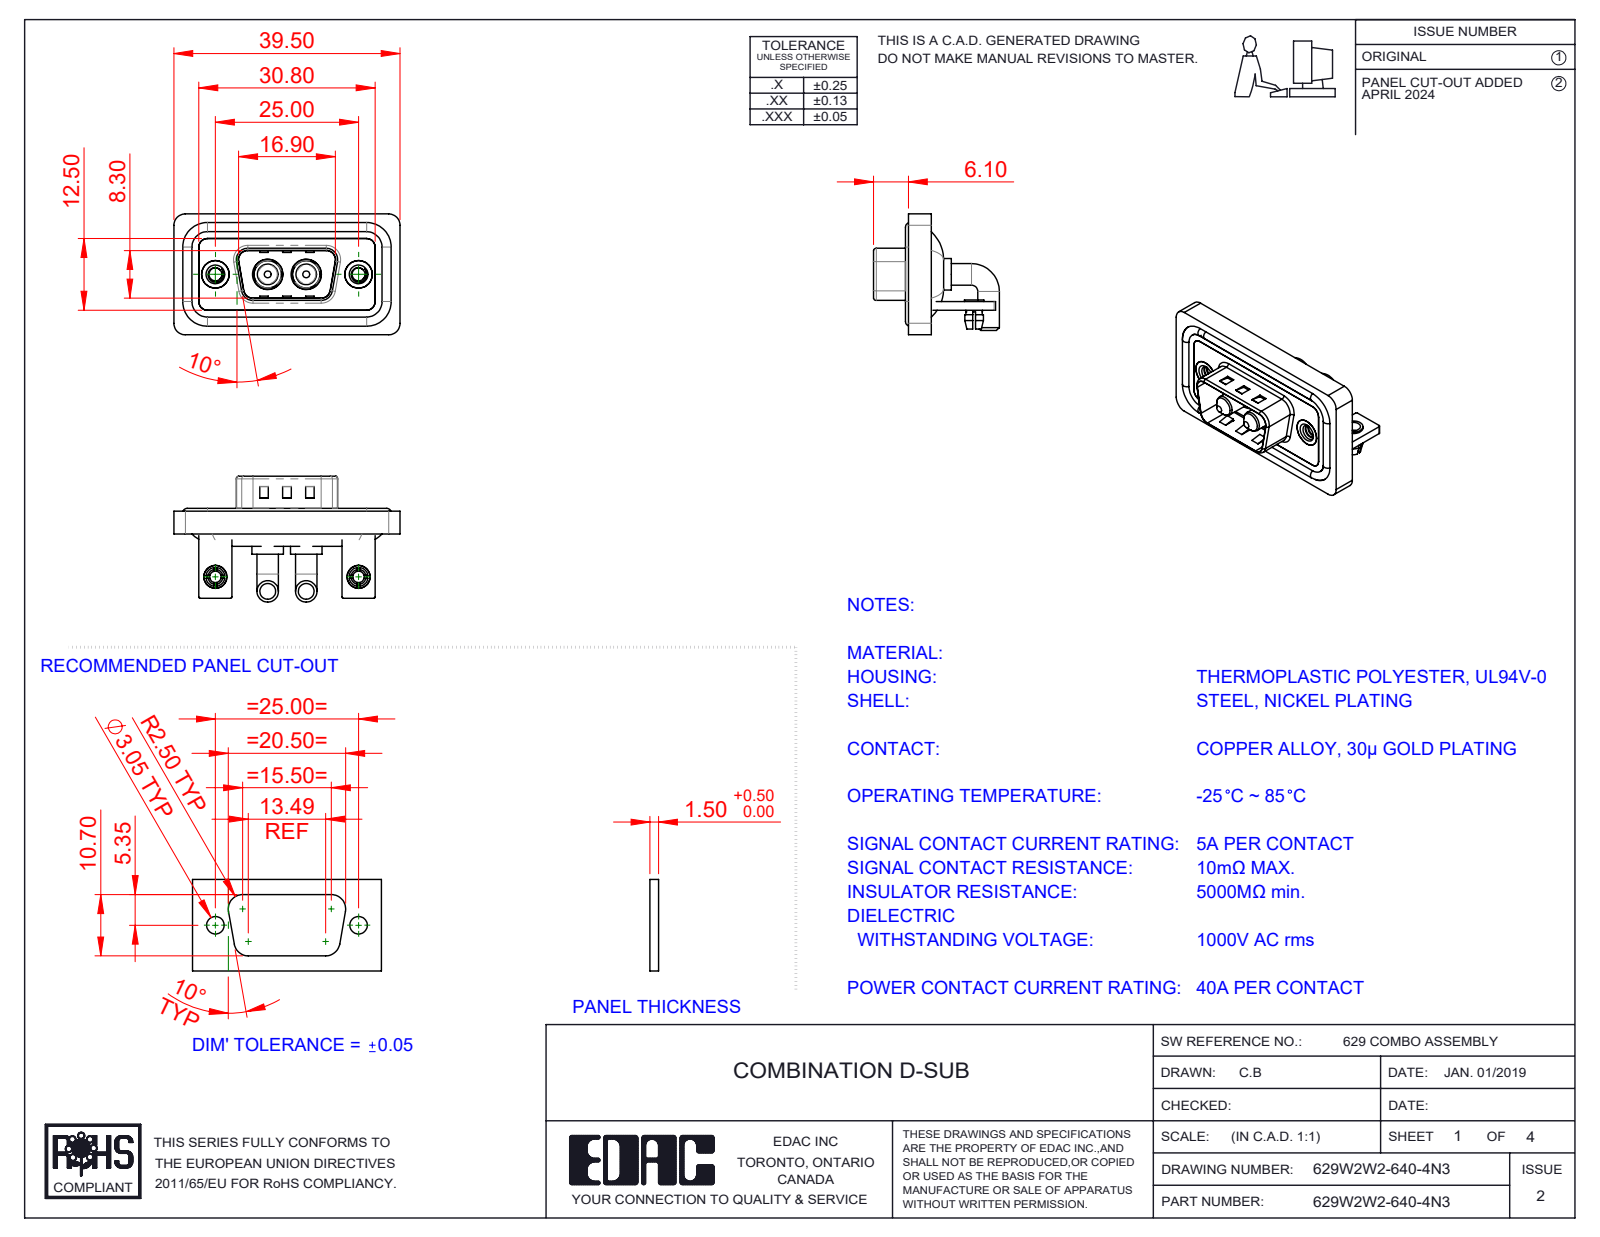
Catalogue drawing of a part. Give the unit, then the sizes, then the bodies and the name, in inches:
Units: inches
Overall size (bounding box): 1.555 × 0.865 × 0.831
Round holes (diameter × count): ⌀0.079 ×2, ⌀0.089 ×2, ⌀0.098 ×2, ⌀0.126 ×2, ⌀0.157 ×2, ⌀0.189 ×2, ⌀0.191 ×2, ⌀0.197 ×2, ⌀0.209 ×2
Round bosses / shafts (diameter × count): ⌀0.148 ×4, ⌀0.063 ×4, ⌀0.217 ×2, ⌀0.205 ×2, ⌀0.193 ×2, ⌀0.187 ×2, ⌀0.157 ×2, ⌀0.142 ×2
Partial cylindrical surfaces — rounded edges, fillets, slot ends (radius × count): R0.079 ×19, R0.059 ×18, R0.01 ×16, R0.02 ×9, R0.063 ×8, R0.024 ×4, R0.026 ×4, R0.035 ×4
Main face-to-face distances: 0.016, 0.059, 0.114, 0.031, 0.043, 0.047, 0.083, 0.063, 0.146, 0.098
Hole centre spacings: 0.36, 0.624, 0.984, 0.265
Volume: 0.308 in³ · Surface area: 12.48 in²
Bodies: 15 solids, 629 faces (233 planar, 272 cylindrical, 124 other)
Part name (STEP PRODUCT): 629Combo Housing_2W2; 629Combo Waterproof Housing_09 Contacts; 629Combo Threaded Rivet_3; 629Combo Shell Rear_09 Contacts (+5 more)
STEP written by: SolidWorks 2023 (CONFIG_CONTROL_DESIGN)
